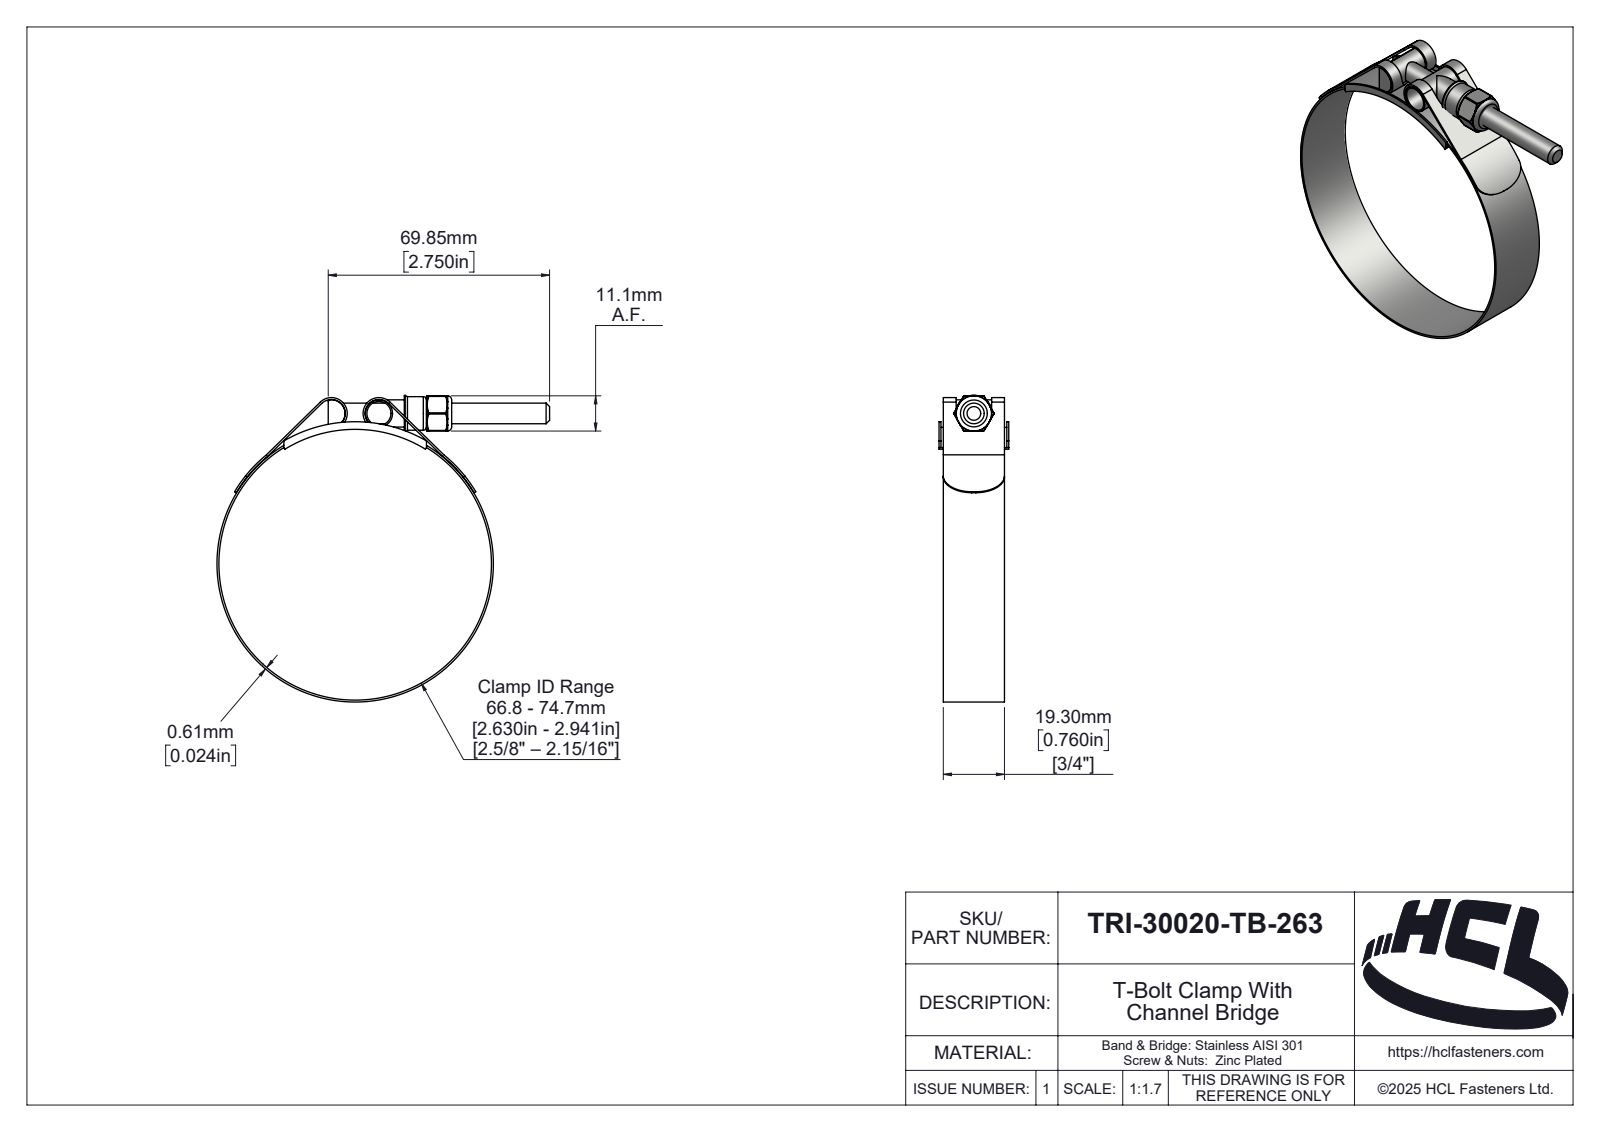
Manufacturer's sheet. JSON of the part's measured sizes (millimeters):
{"part_name": "TRI-30020-TB-263", "step_written_by": "SolidWorks 2025 (AUTOMOTIVE_DESIGN)", "units": "millimeters", "bodies": {"solids": 6, "faces": 330, "planar": 44, "cylindrical": 122, "other": 164}, "overall_size": [104.96, 96.74, 22], "volume_mm3": 8928, "surface_area_mm2": 20523, "round_holes": [[5.4, 1], [6.35, 1], [6.5, 1], [7.58, 1], [86, 1]], "round_bosses_or_shafts": [[8.58, 2], [87.22, 1], [10.58, 1]], "partial_cylinders_radius": [[0.39, 6], [0.5, 2], [4.39, 2], [5, 2], [0.59, 1], [2.42, 1], [3.03, 1], [3.19, 1]], "face_to_face_distances": [0.61, 19.3, 1.35, 20.65, 0.74, 21.39, 20.04, 22, 20.78, 31], "hole_center_spacings": [48]}
